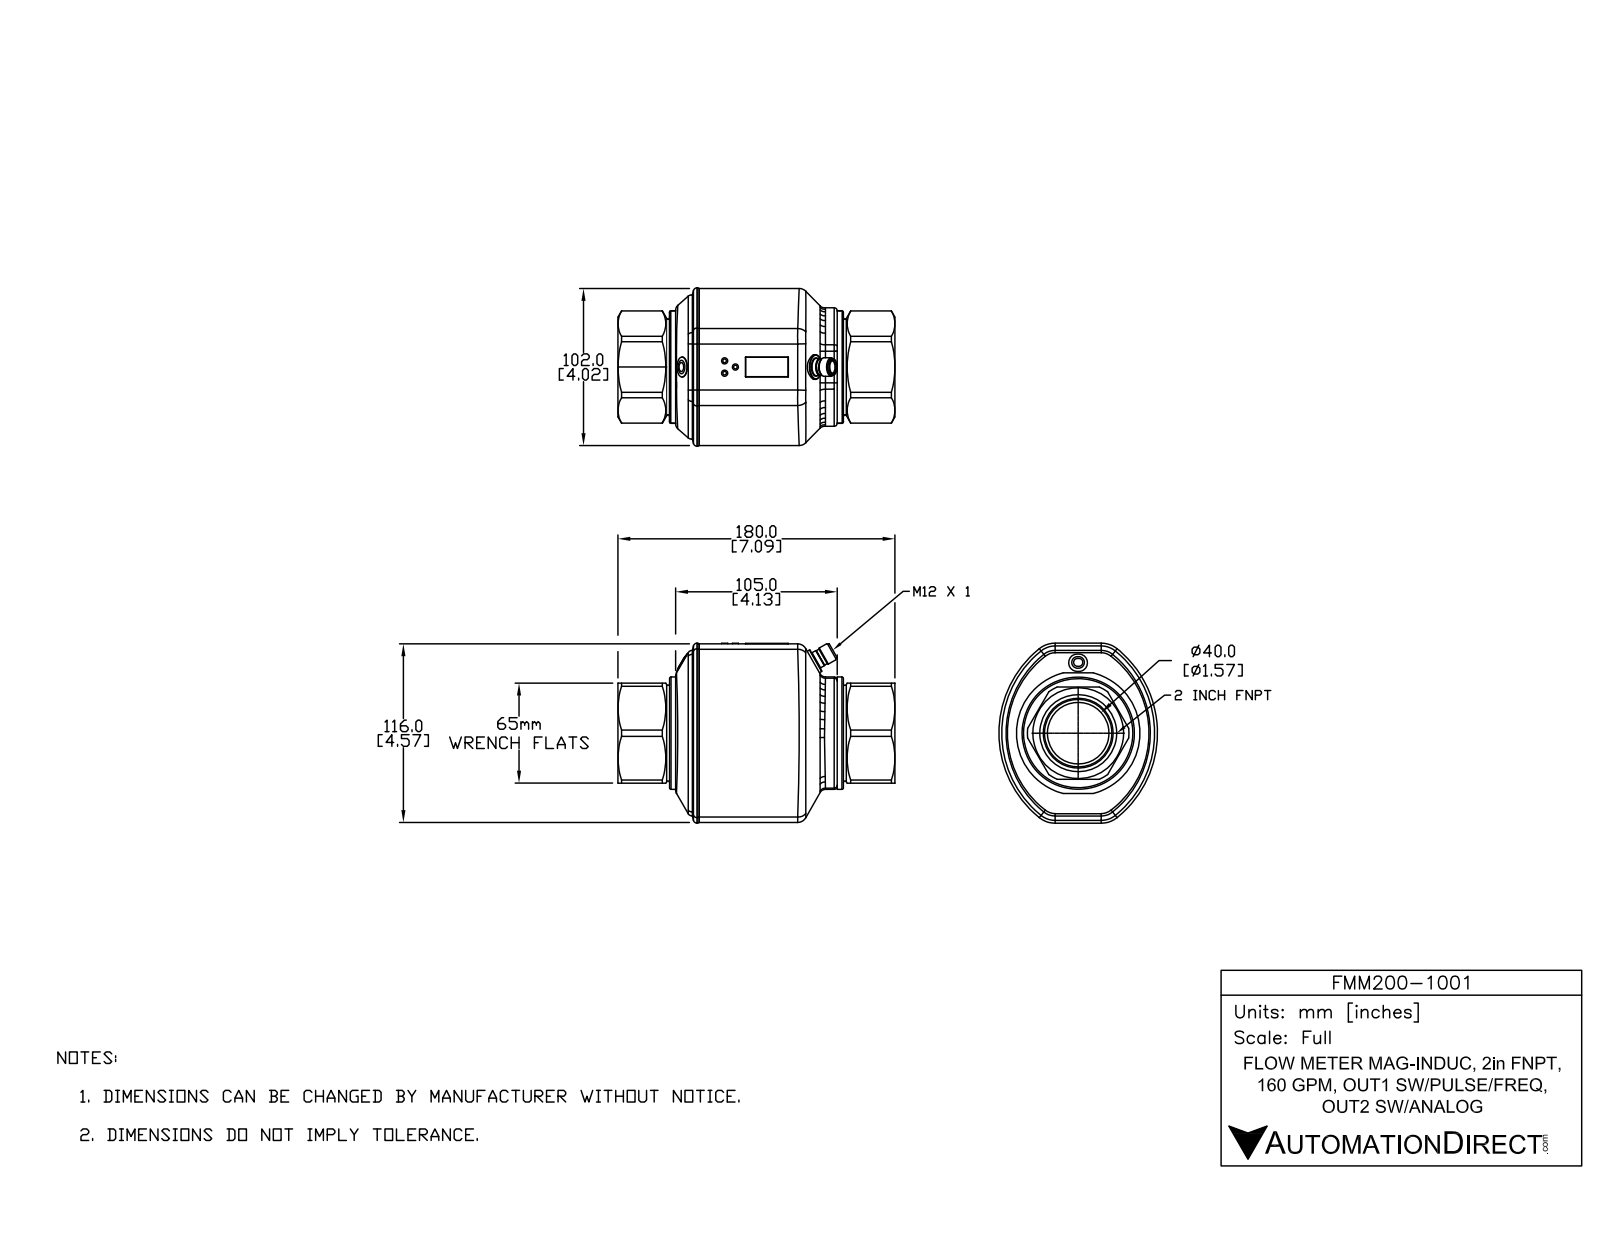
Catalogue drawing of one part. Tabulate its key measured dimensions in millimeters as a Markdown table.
| quantity | value |
| --- | --- |
| part name | FMM200-1001 |
| STEP written by | SolidWorks 2015 (AUTOMOTIVE_DESIGN) |
| units | millimeters |
| bodies | 10 solids, 289 faces (81 planar, 84 cylindrical, 124 other) |
| overall size | 186.28 × 118.91 × 103 |
| volume | 1 085 000 mm³ |
| surface area | 125 550 mm² |
| round holes (diameter × count) | 8.4 × 1, 40 × 1, 56 × 1 |
| round bosses / shafts (diameter × count) | 4 × 3, 12 × 2, 3.9 × 2, 73 × 1, 64 × 1, 14.9 × 1, 11.3 × 1, 10.6 × 1 |
| partial cylindrical surfaces (radius × count) | 0.9 × 4, 11 × 4, 16 × 4, 16.5 × 4, 1 × 2, 2 × 2, 70 × 2, 70.5 × 2 |
| main face-to-face distances | 23.91, 79.3, 103.21, 110.88, 31.58, 7.67, 65, 25.5, 90.5, 4.87 |
